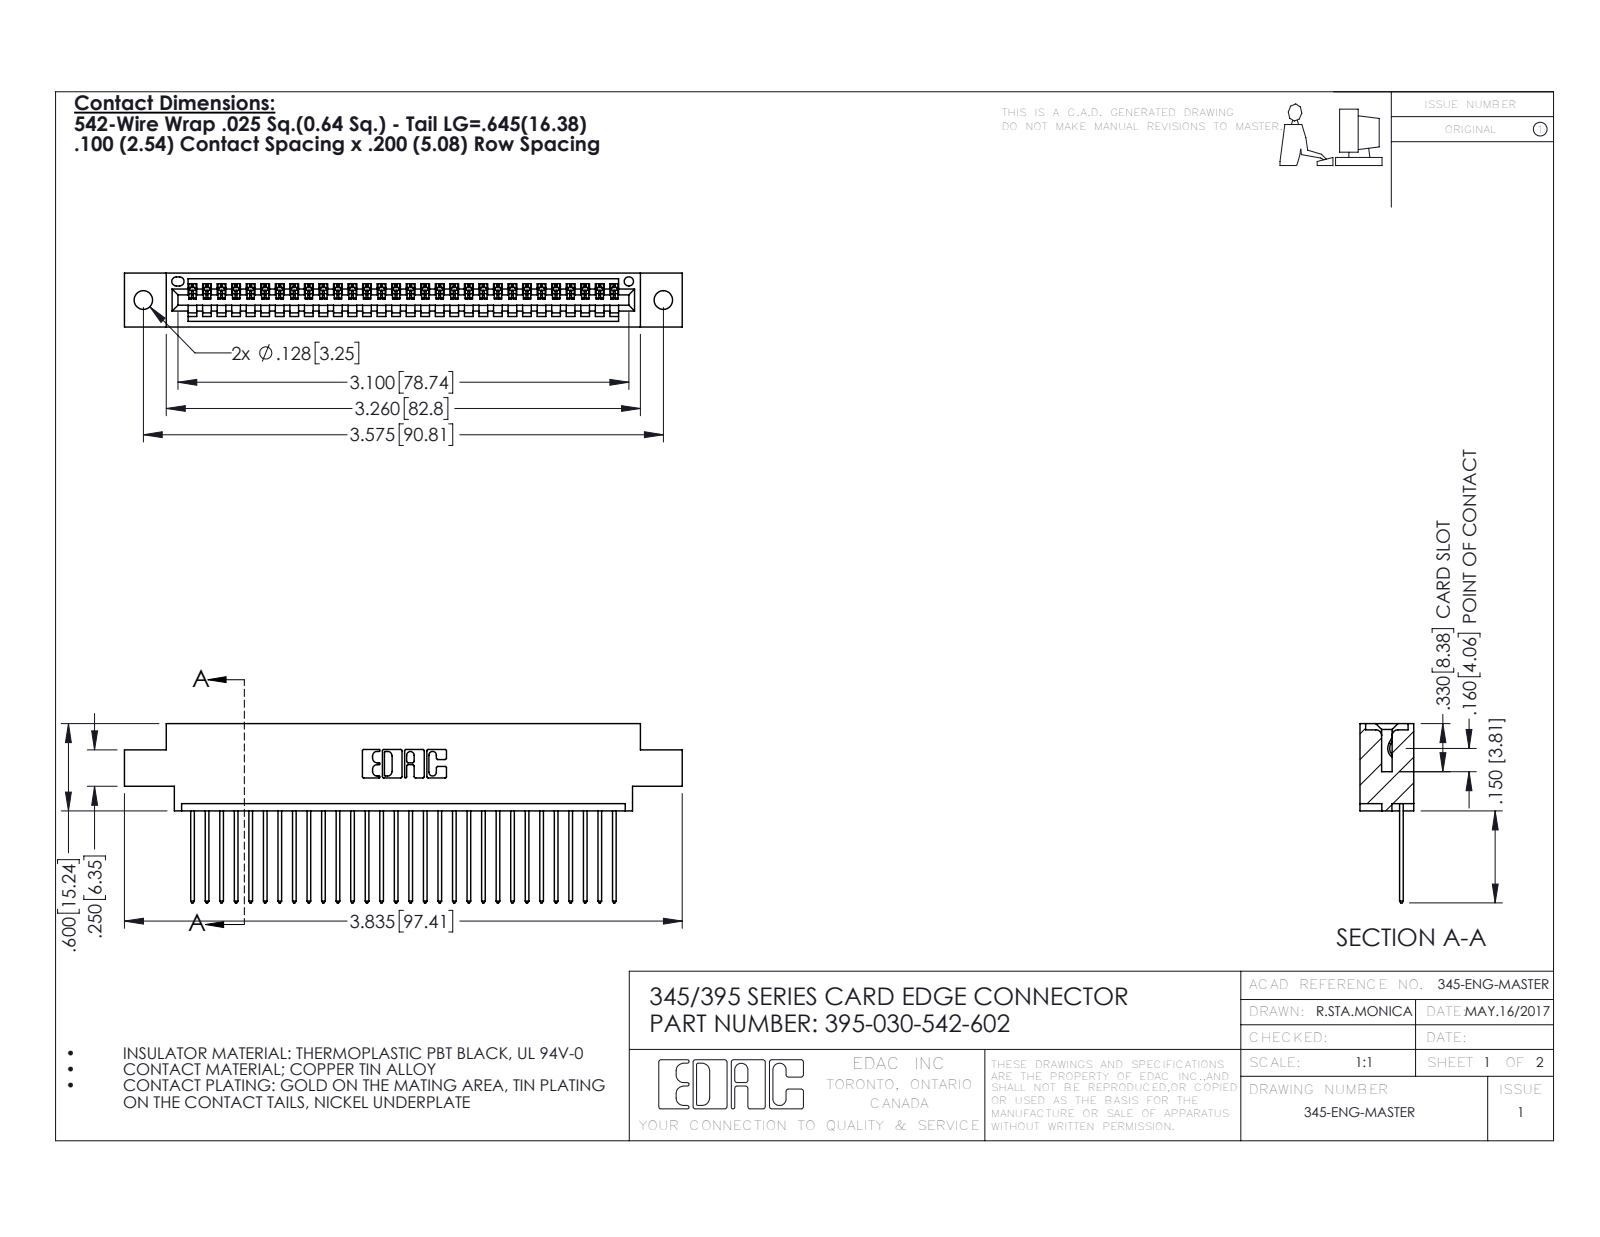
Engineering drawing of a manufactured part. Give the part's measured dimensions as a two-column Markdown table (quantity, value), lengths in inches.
| quantity | value |
| --- | --- |
| part name | 395-030-542-602; 345-292-001_345-293-142; 345 Part_0.170 Offset - 0.128 Dia |
| STEP written by | SolidWorks 2016 (CONFIG_CONTROL_DESIGN) |
| units | inches |
| bodies | 31 solids, 1870 faces (1284 planar, 586 cylindrical, 0 other) |
| overall size | 3.835 × 1.232 × 0.37 |
| volume | 0.554 in³ |
| surface area | 18.86 in² |
| round holes (diameter × count) | 0.128 × 2, 0.064 × 1 |
| partial cylindrical surfaces (radius × count) | 0.006 × 60, 0.01 × 60, 0.01 × 22, 0.007 × 6, 0.031 × 6, 0.026 × 3, 0.031 × 2, 0.04 × 2 |
| main face-to-face distances | 0.298, 0.072, 0.37, 0.098, 0.272, 0.025, 0.2, 0.225, 0.175, 0.149 |
| hole center spacings | 0.27, 3.34, 3.575 |
